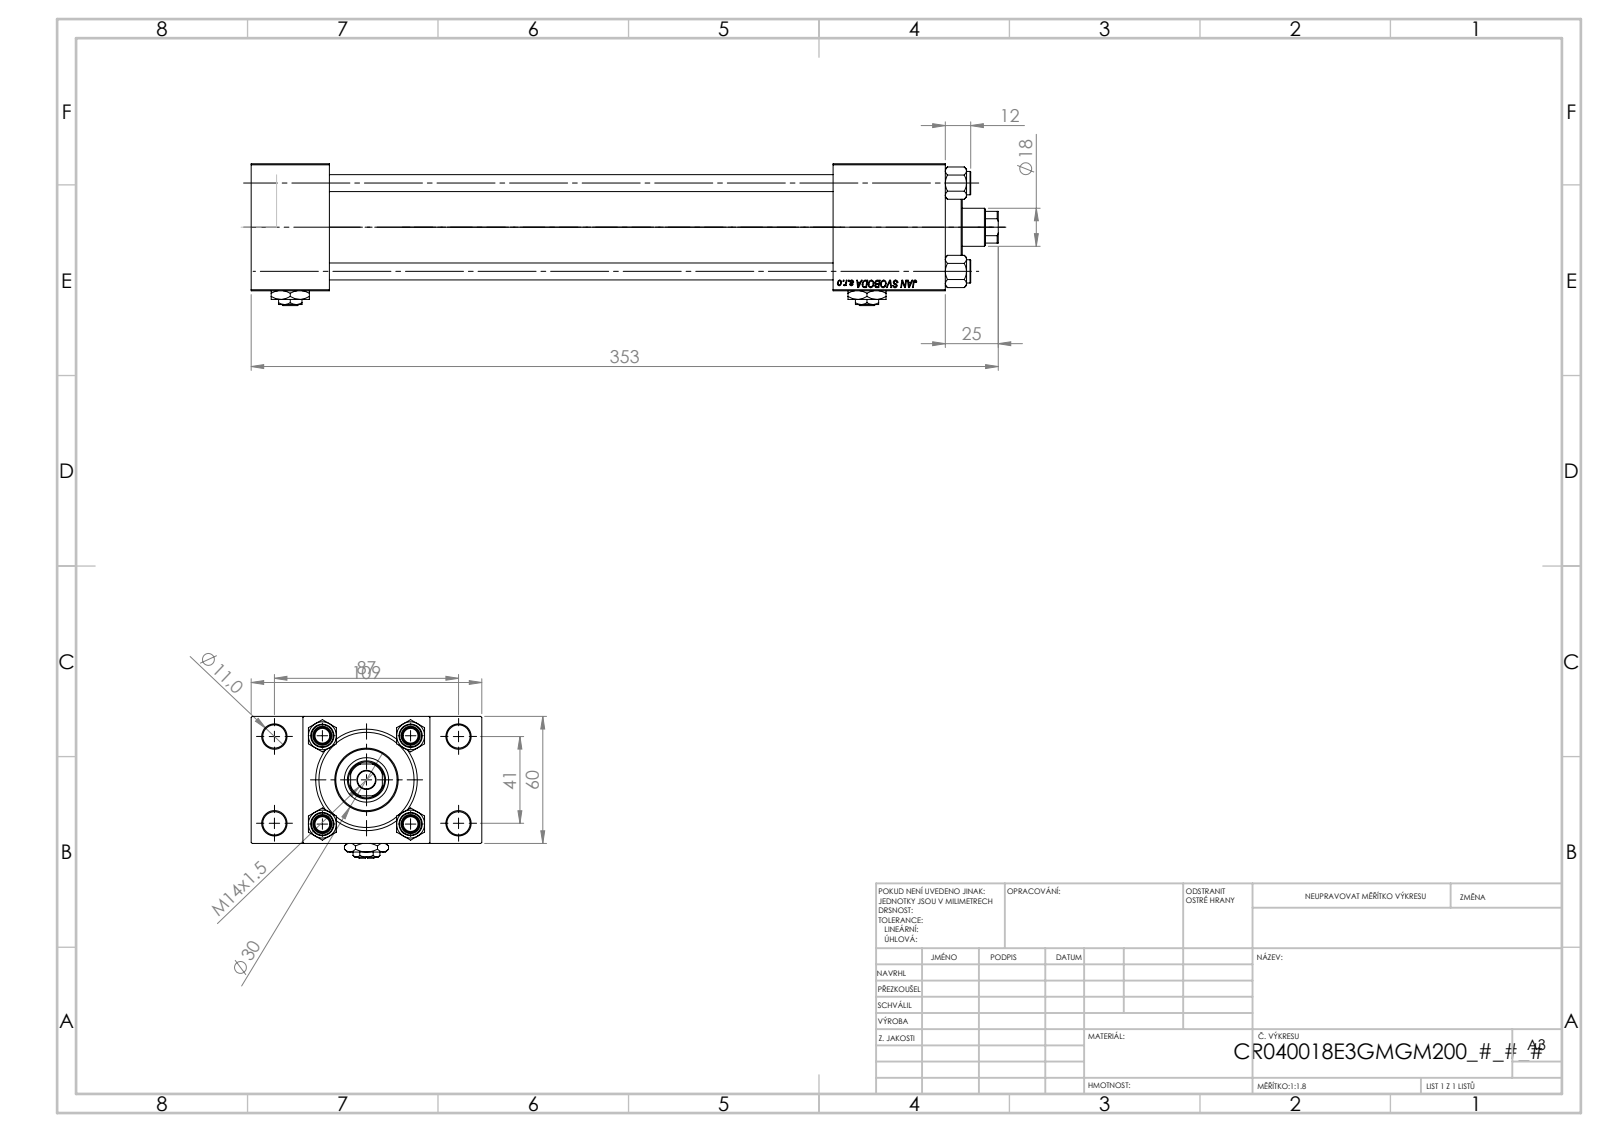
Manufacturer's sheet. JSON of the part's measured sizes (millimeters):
{"part_name": "V215_VC_A; V215CR_VCP_E; V215CR_TYCINKA_E; Zatka_pro_OIL_PORT (+2 more)", "step_written_by": "SolidWorks 2019 (CONFIG_CONTROL_DESIGN)", "units": "millimeters", "bodies": {"solids": 13, "faces": 1237, "planar": 546, "cylindrical": 97, "other": 594}, "overall_size": [353, 109, 67], "volume_mm3": 651149, "surface_area_mm2": 204280, "round_holes": [[8, 4], [11, 4], [16.66, 4], [24, 4], [7, 3], [8.5, 1], [18, 1], [21, 1], [31, 1], [40, 1], [45, 1]], "round_bosses_or_shafts": [[11, 4], [46, 1], [30, 1]], "partial_cylinders_radius": [[8.5, 1]], "face_to_face_distances": [60, 37, 24.5, 84.5, 328, 291, 24.3, 53, 275, 238], "hole_center_spacings": [22.65, 29.49, 41.7, 47.15, 48.09, 64.35, 76.49, 41]}
